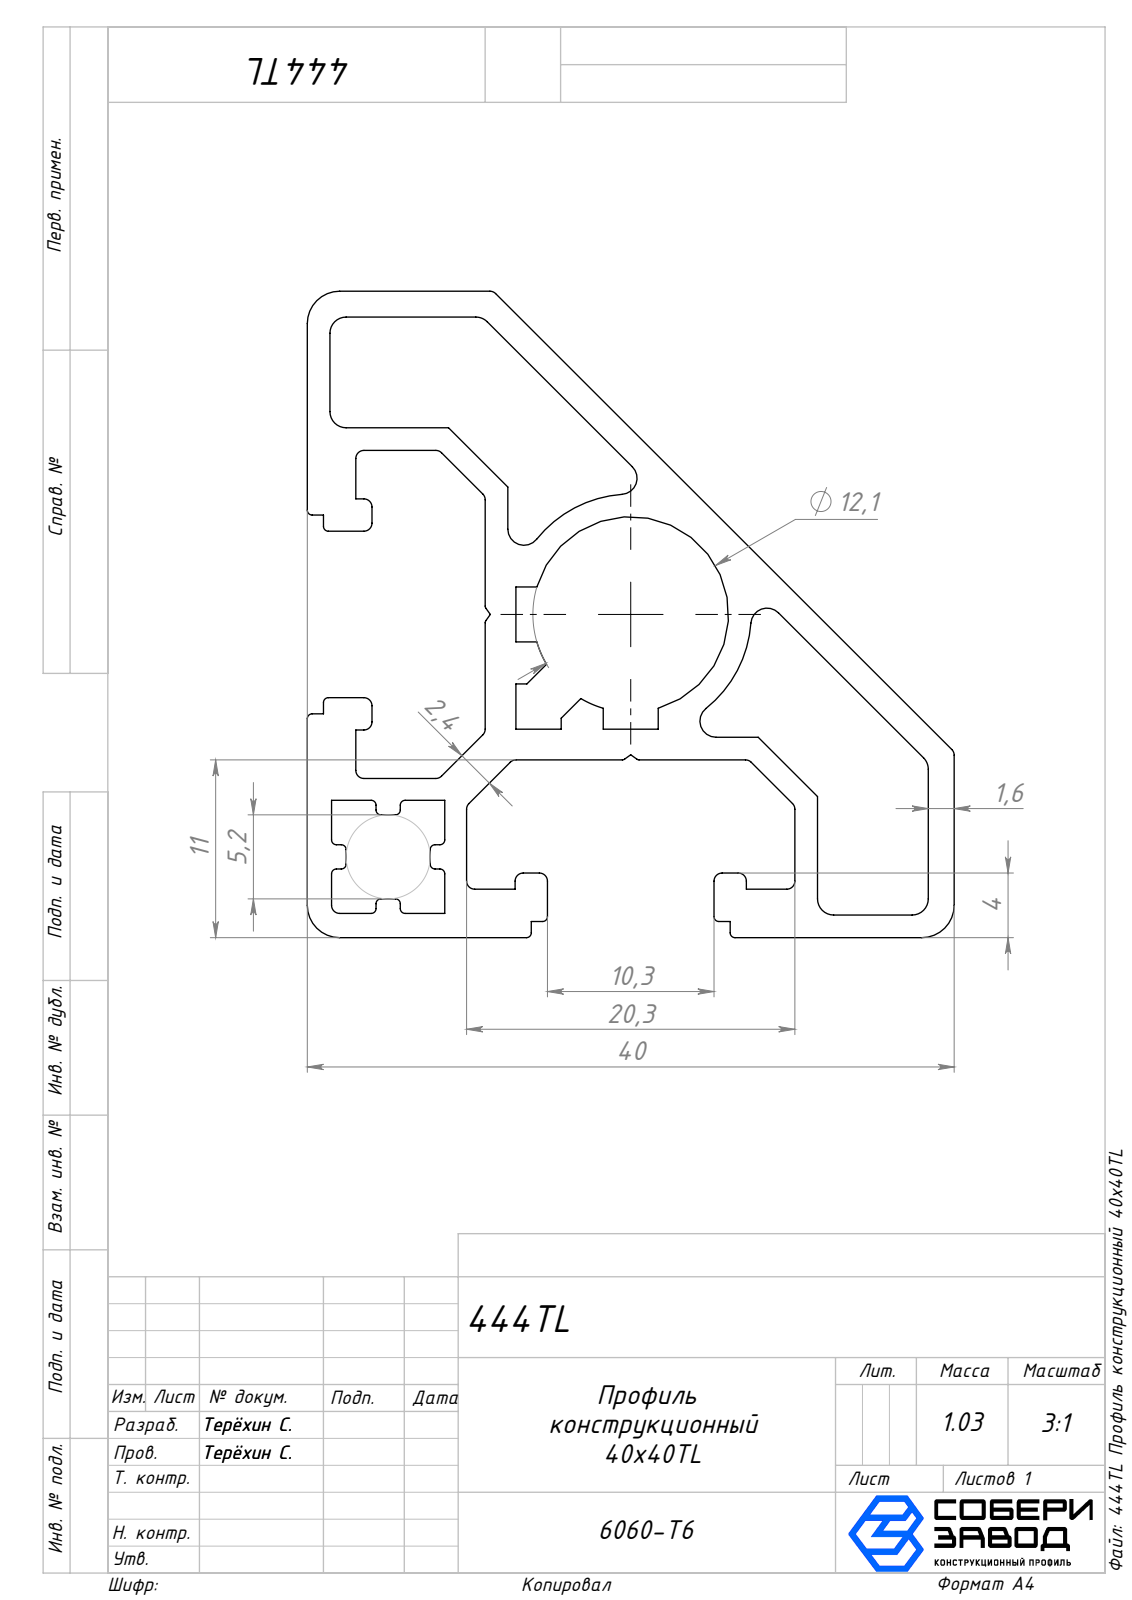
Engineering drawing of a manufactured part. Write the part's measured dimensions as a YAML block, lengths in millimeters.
part_name: "Сборка10; 444TL Профиль конструкционный 40х40TL_00"
step_written_by: "SolidWorks 2024 (AUTOMOTIVE_DESIGN)"
units: millimeters
bodies: {solids: 1, faces: 163, planar: 93, cylindrical: 70, other: 0}
overall_size: [1000, 40, 40]
volume: 380552
surface_area: 415780
partial_cylinders:
  - {radius: 0.3, count: 24}
  - {radius: 0.5, count: 23}
  - {radius: 1, count: 10}
  - {radius: 0.25, count: 4}
  - {radius: 2, count: 3}
  - {radius: 6.05, count: 1}
  - {radius: 7.45, count: 1}
face_to_face_distances: [1.6, 1.4, 11, 30.15, 8.45, 6.85, 9.85, 37, 28.55, 40]
